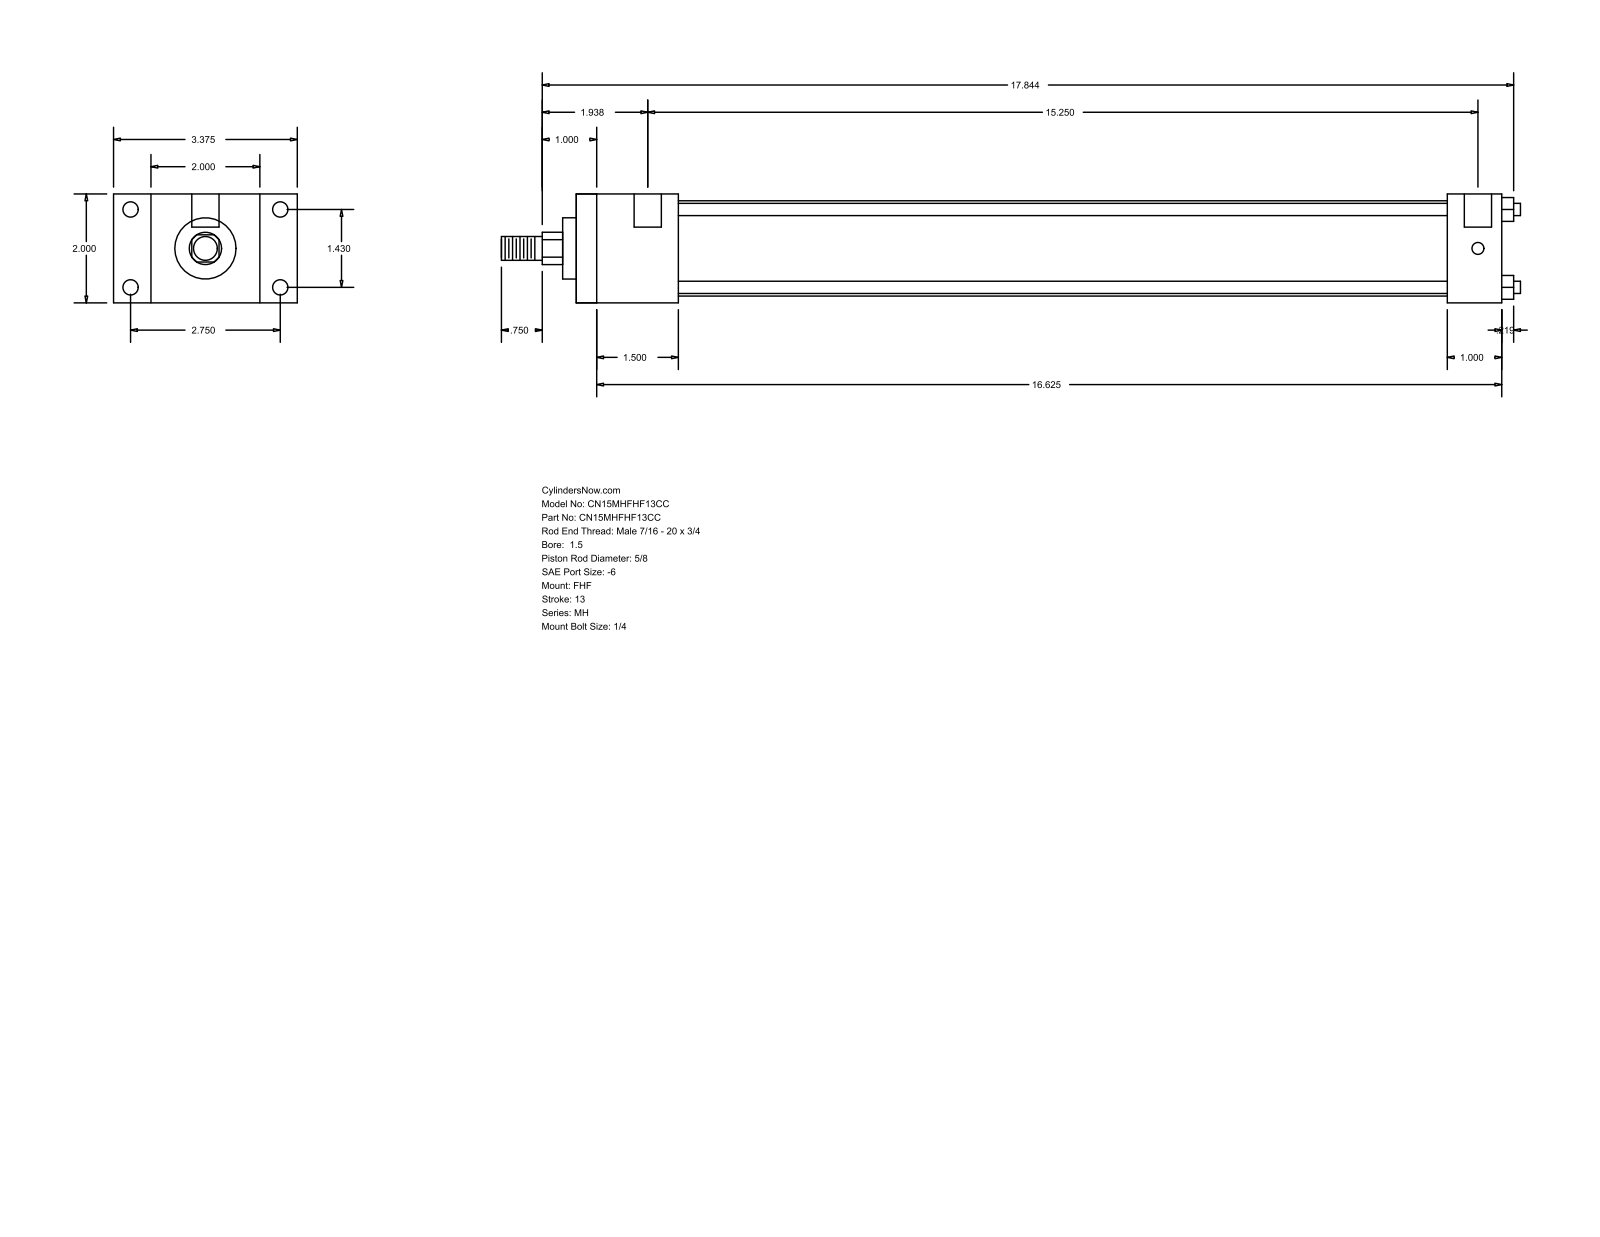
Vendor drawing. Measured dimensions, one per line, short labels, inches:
name: MH_FHF__0150_0.625
written by: GSSL Pune (CONFIG_CONTROL_DESIGN)
unit: in
bodies: 0 solids, 88 faces (60 planar, 28 cylindrical, 0 other)
size: 18.719 × 3.375 × 2
holes: 4× ⌀0.219, 4× ⌀0.281, 2× ⌀0.5
bosses: 4× ⌀0.225, 1× ⌀1.75, 1× ⌀1.125, 1× ⌀0.625, 1× ⌀0.437
rounds: 1× R0.297
face distances: 2, 0.687, 2.687, 1.875, 3.375, 17, 15.125, 16, 14.125, 1
hole spacings: 1.43, 2.75, 3.099, 15.375, 0.125, 15.25
